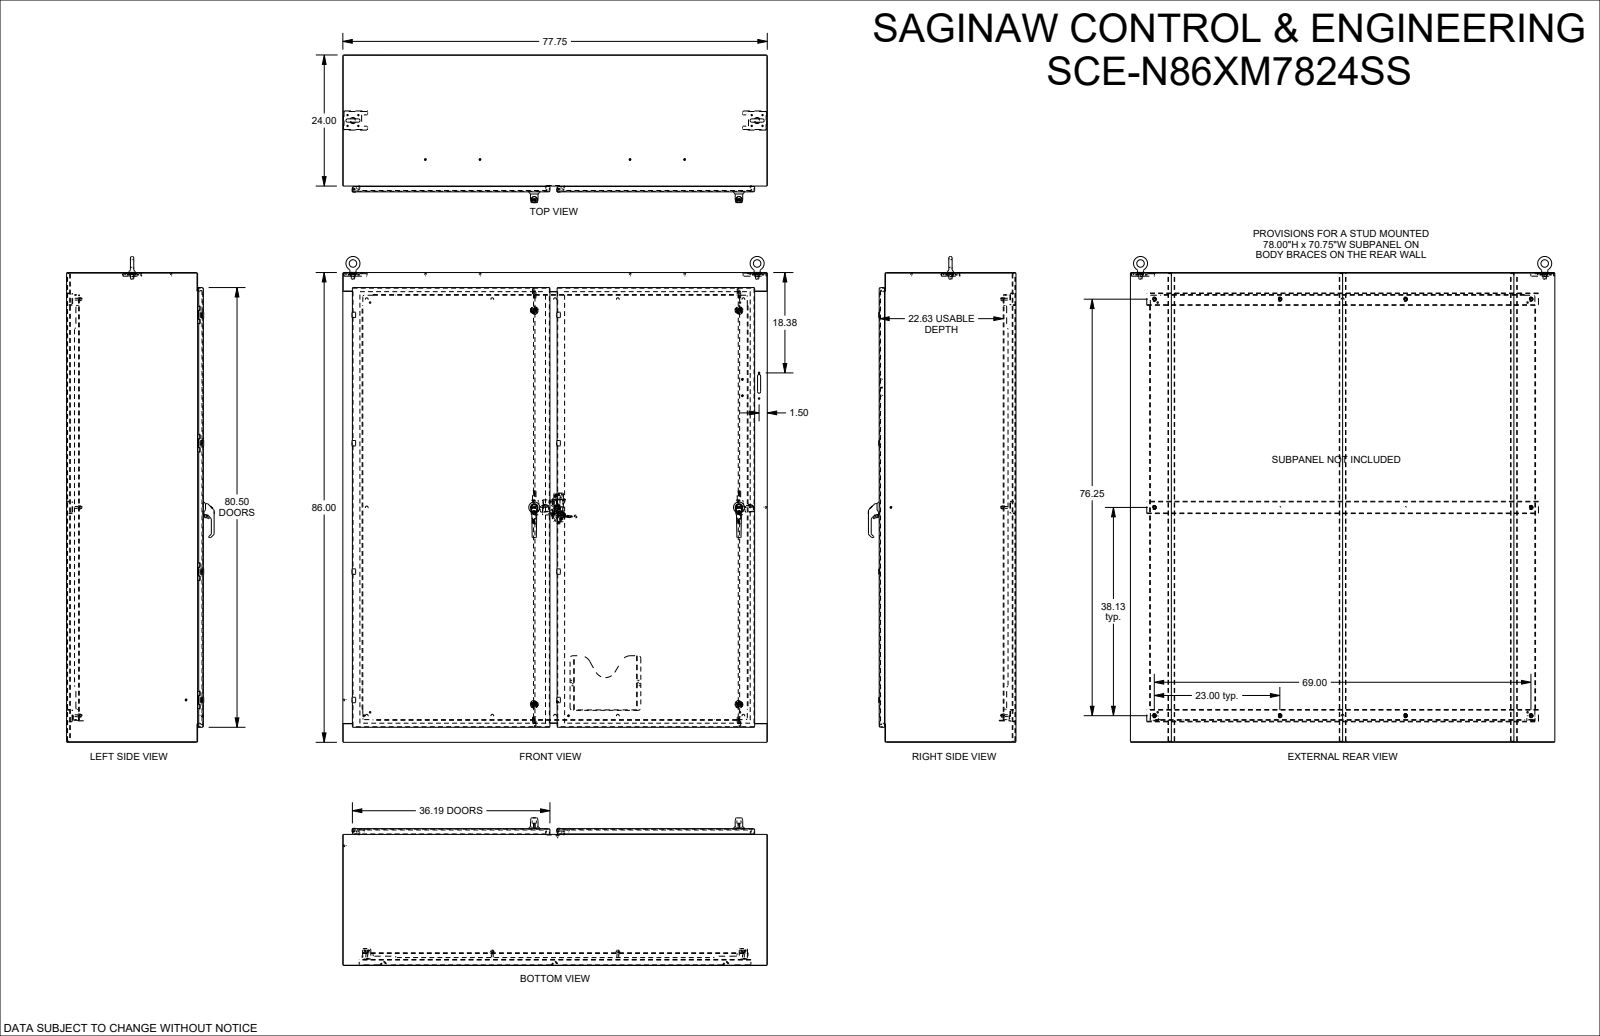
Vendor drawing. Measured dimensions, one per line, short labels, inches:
name: SCE-N86XM7824_REV1
written by: SolidWorks 2023 (AUTOMOTIVE_DESIGN)
unit: in
bodies: 48 solids, 7346 faces (3045 planar, 2479 cylindrical, 1822 other)
size: 88.945 × 77.75 × 27.046
volume: 2 583 in³; area: 49 293 in²
holes: 16× ⌀0.205, 16× ⌀0.244, 14× ⌀0.25, 8× ⌀0.04, 8× ⌀0.17, 8× ⌀0.218, 8× ⌀0.375, 8× ⌀0.375, 4× ⌀0.256, 4× ⌀0.343, 4× ⌀0.344, 4× ⌀0.36
bosses: 24× ⌀0.17, 19× ⌀0.25, 16× ⌀0.24, 10× ⌀0.196, 4× ⌀1.4, 4× ⌀0.341, 2× ⌀2.008, 2× ⌀1.173
rounds: 208× R0.03, 166× R0.015, 66× R0.125, 65× R0.02, 57× R0.04, 48× R0.02, 43× R0.25, 42× R0.039
face distances: 0.104, 24.954, 24.85, 25.058, 77.646, 85.896, 23.896, 1.058, 77.75, 77.542
hole spacings: 23.5, 44.255, 47, 35.431, 60.127, 0.493, 0.494, 0.984
